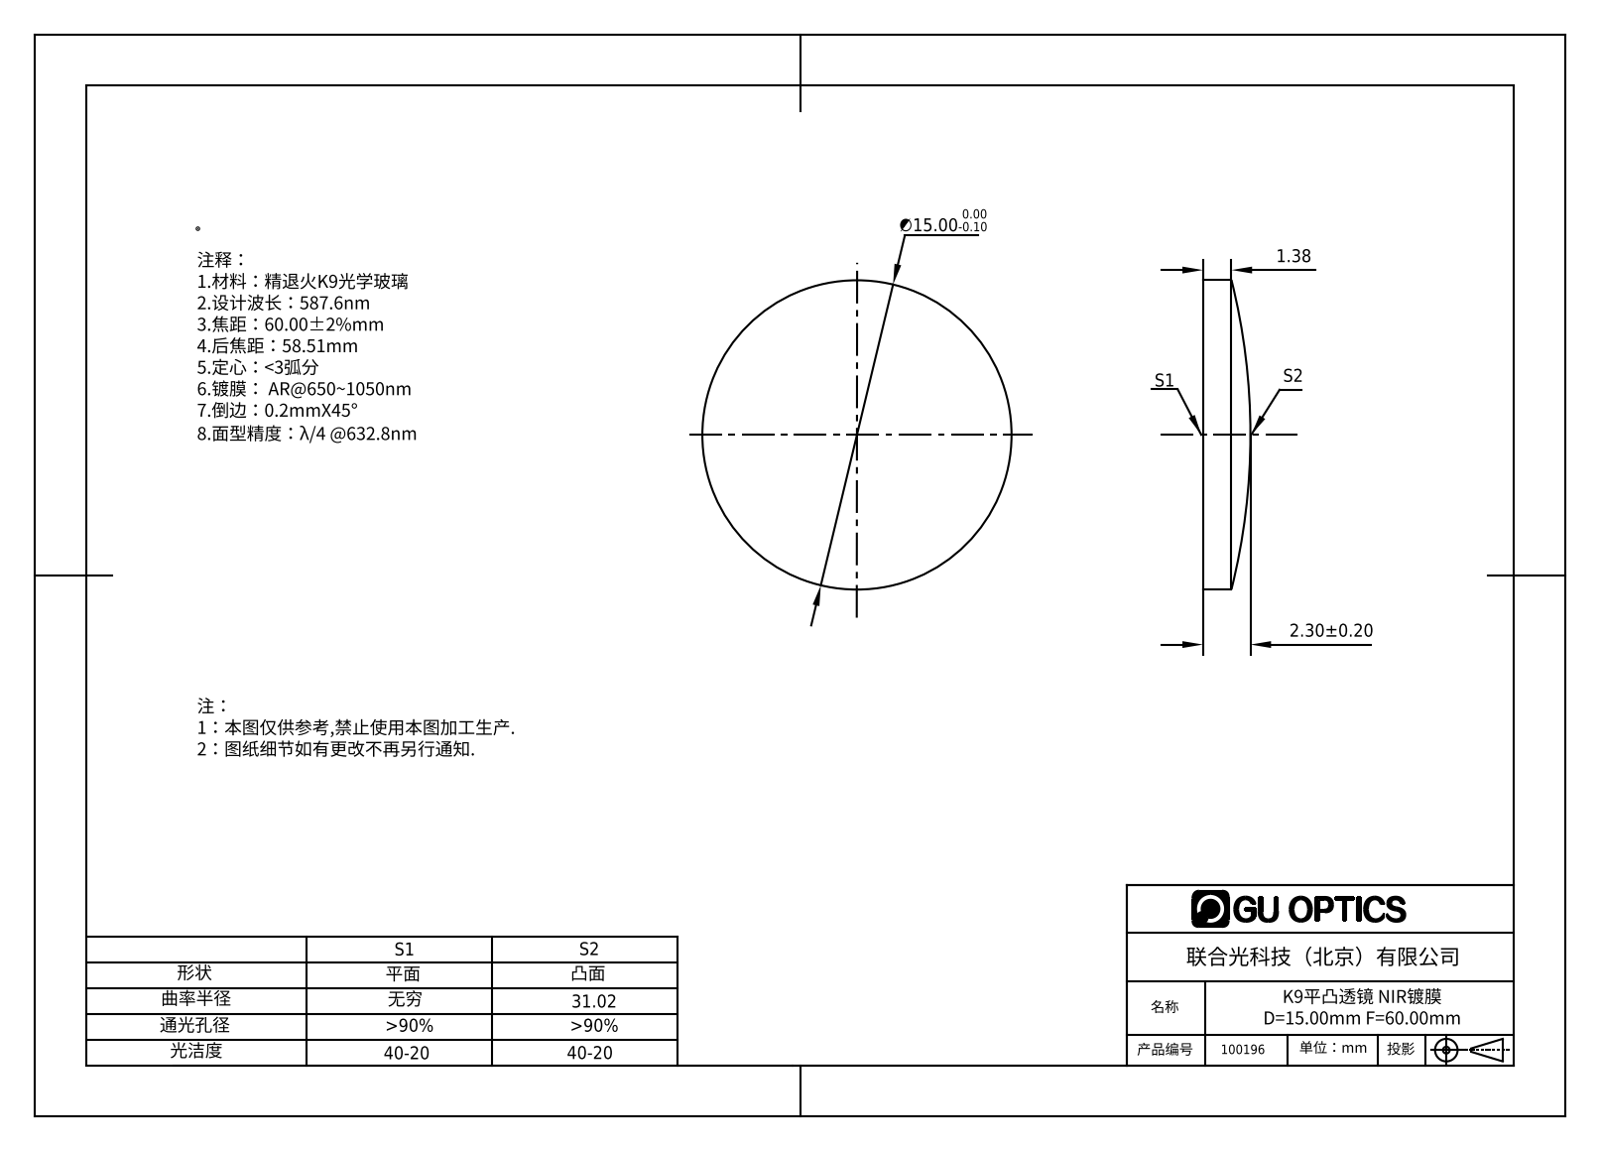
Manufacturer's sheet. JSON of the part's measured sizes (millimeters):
{"part_name": "100196", "step_written_by": "SolidWorks 2016 (AUTOMOTIVE_DESIGN)", "units": "millimeters", "bodies": {"solids": 1, "faces": 5, "planar": 1, "cylindrical": 2, "other": 2}, "overall_size": [15, 15, 2.3], "volume_mm3": 326, "surface_area_mm2": 421, "round_bosses_or_shafts": [[15, 1]]}
